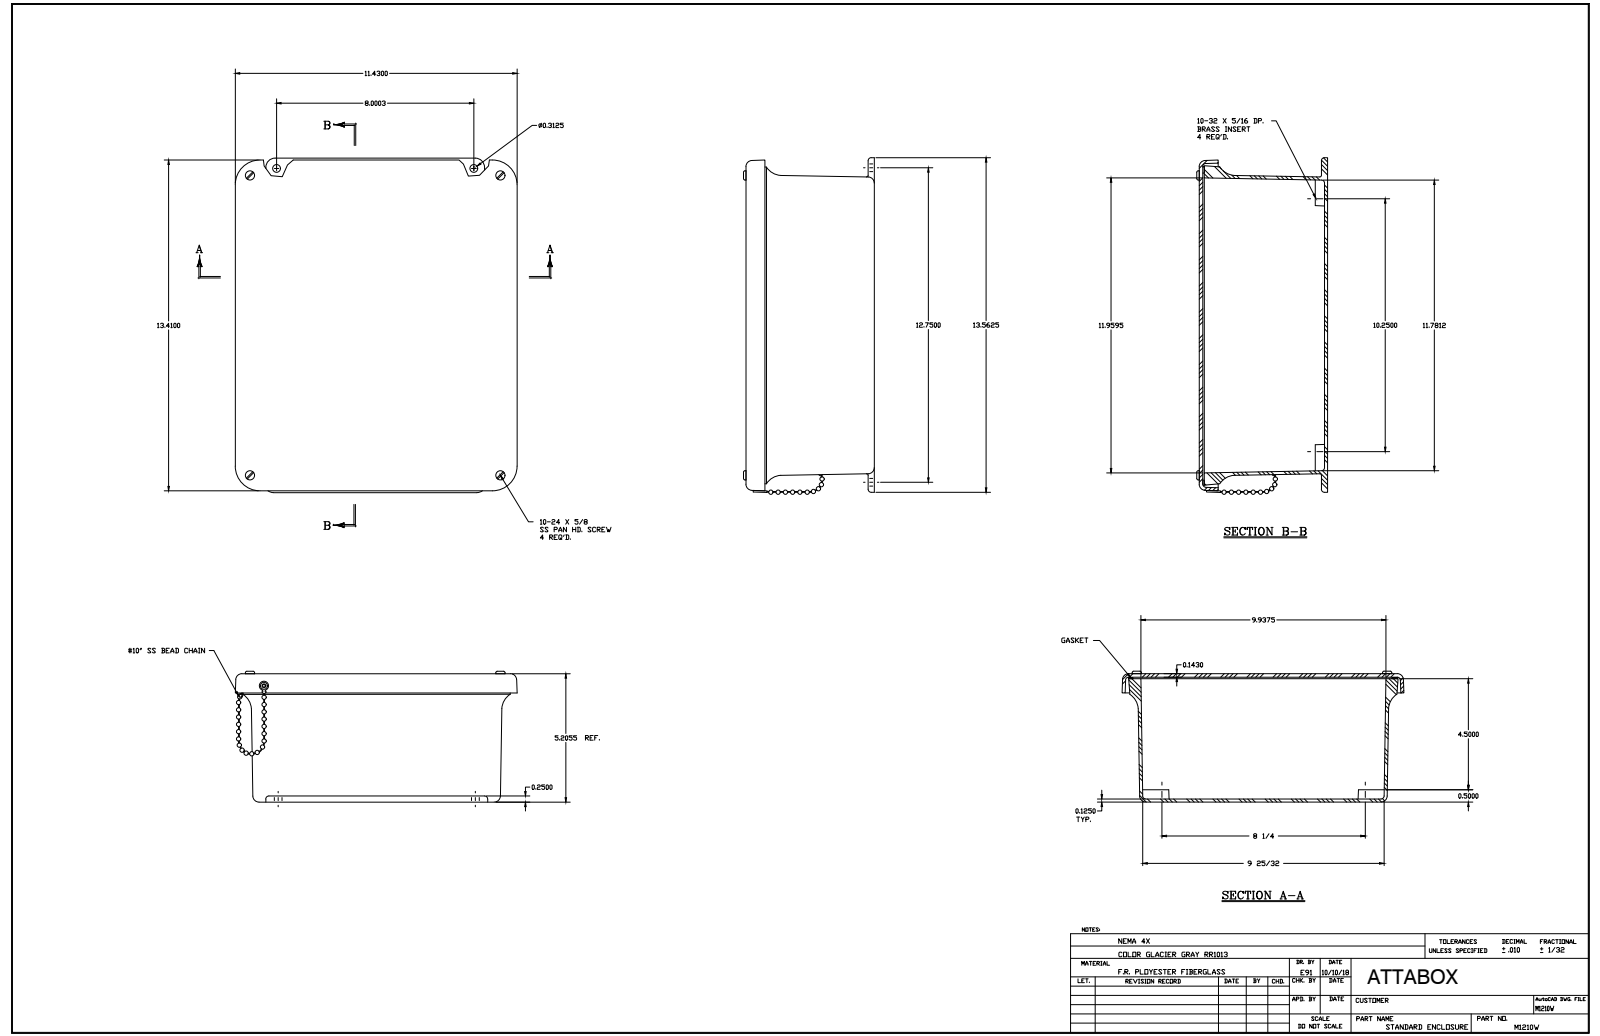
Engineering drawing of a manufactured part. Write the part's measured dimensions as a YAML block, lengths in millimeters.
part_name: "M1210W"
step_written_by: "SolidWorks 2018 (AUTOMOTIVE_DESIGN)"
units: millimeters
bodies: {solids: 45, faces: 886, planar: 187, cylindrical: 287, other: 412}
overall_size: [356.8, 296.5, 135.9]
volume: 1411000
surface_area: 731600
round_holes:
  - {diameter: 3.6, count: 5}
  - {diameter: 3.9, count: 5}
  - {diameter: 3.7, count: 4}
  - {diameter: 4, count: 4}
  - {diameter: 5.5, count: 4}
  - {diameter: 4.7, count: 2}
  - {diameter: 3.2, count: 1}
round_bosses_or_shafts:
  - {diameter: 6.9, count: 8}
  - {diameter: 4.8, count: 4}
  - {diameter: 4, count: 4}
  - {diameter: 9.5, count: 2}
  - {diameter: 6.4, count: 2}
  - {diameter: 7.2, count: 1}
  - {diameter: 3.2, count: 1}
  - {diameter: 3.2, count: 1}
partial_cylinders:
  - {radius: 0.8, count: 20}
  - {radius: 3.2, count: 14}
  - {radius: 5.1, count: 8}
  - {radius: 6.4, count: 8}
  - {radius: 9.5, count: 4}
  - {radius: 19.1, count: 4}
  - {radius: 0.3, count: 2}
  - {radius: 1.6, count: 2}
face_to_face_distances: [3.6, 3.2, 128.9, 132.6, 125.8, 129.4, 123.8, 5.6, 127, 1.9]
hole_center_spacings: [235, 34.2, 34.2, 92.1, 174.6, 209.6, 258, 260.4]
